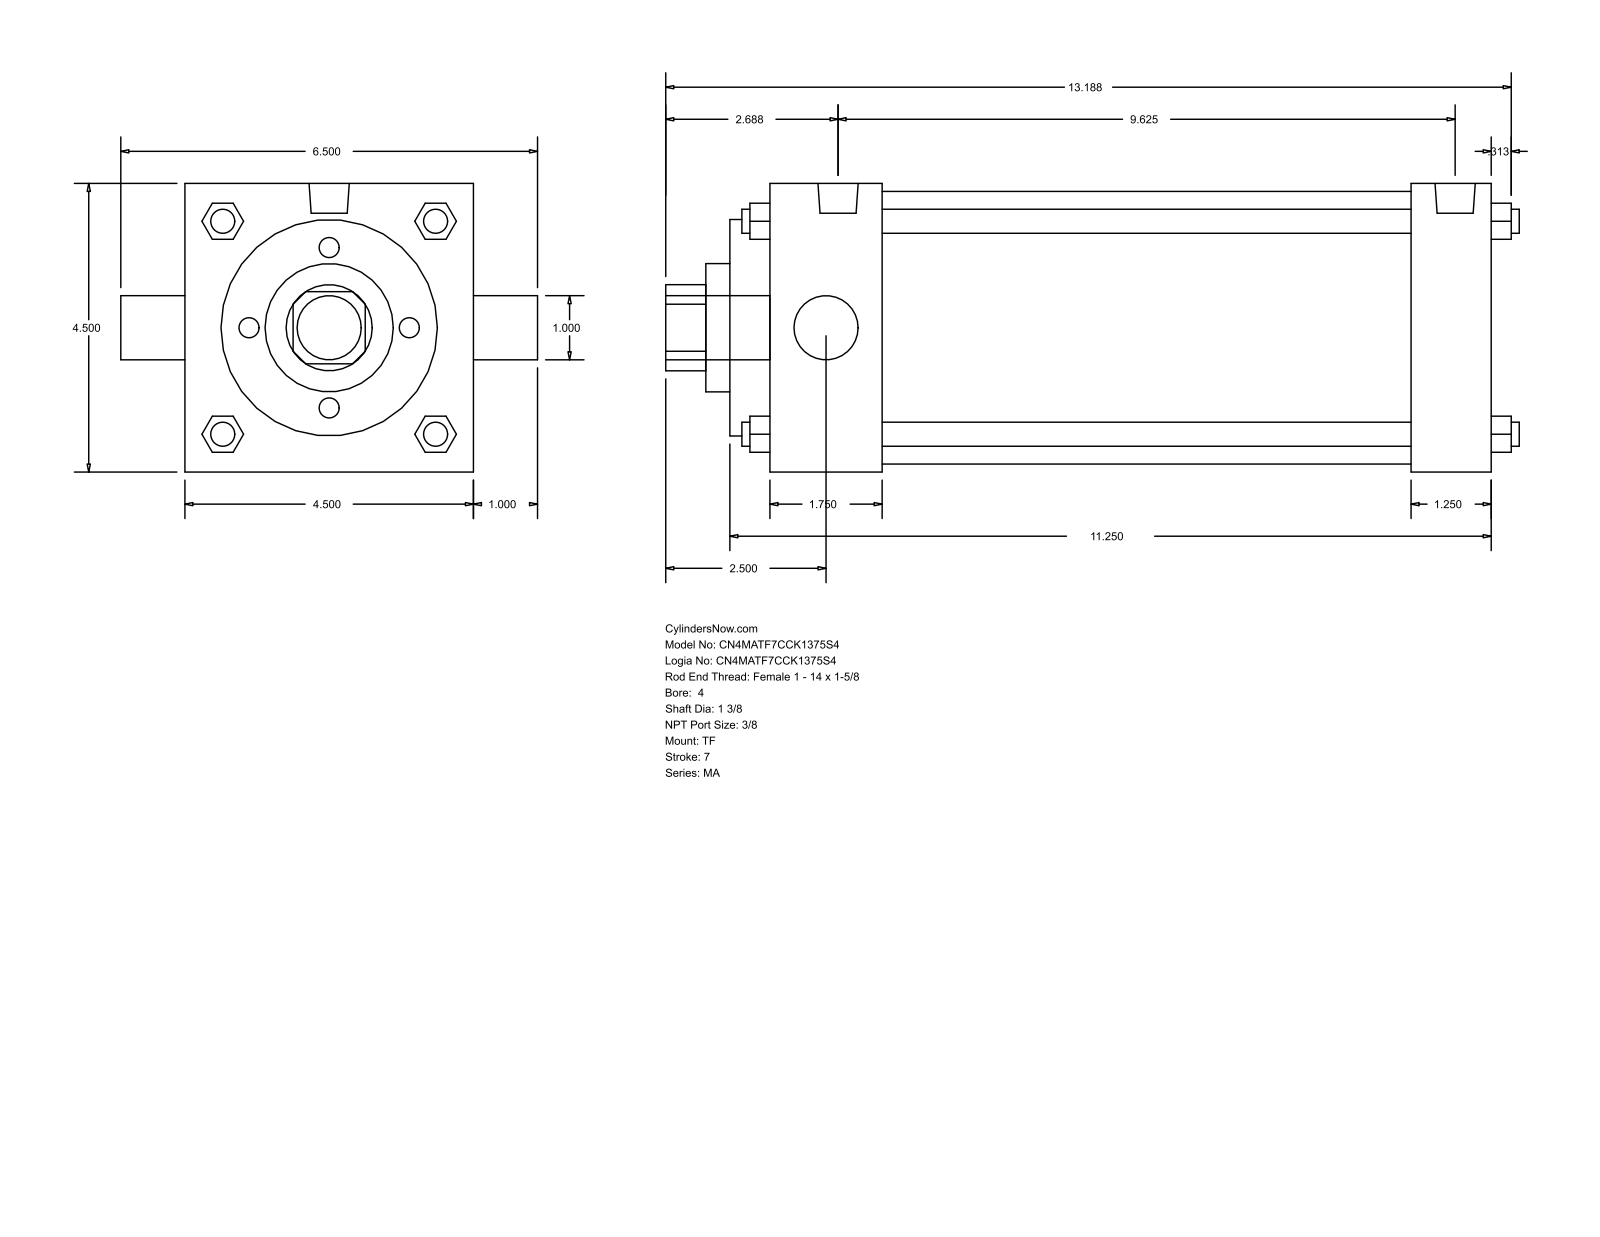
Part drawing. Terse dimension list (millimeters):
name: MA_TF__0400_1.375
written by: GSSL Pune (CONFIG_CONTROL_DESIGN)
unit: mm
bodies: 0 solids, 122 faces (93 planar, 29 cylindrical, 0 other)
size: 338.14 × 165.1 × 114.3
holes: 1× ⌀25.4, 1× ⌀34.92, 1× ⌀50.8, 1× ⌀85.72, 1× ⌀107.95
bosses: 4× ⌀9.53, 3× ⌀11.11, 2× ⌀15.93, 1× ⌀25.4
rounds: 1× R17.06
face distances: 114.3, 285.75, 301.62, 15.87, 269.87, 254, 31.75, 60.32, 44.45, 209.55
